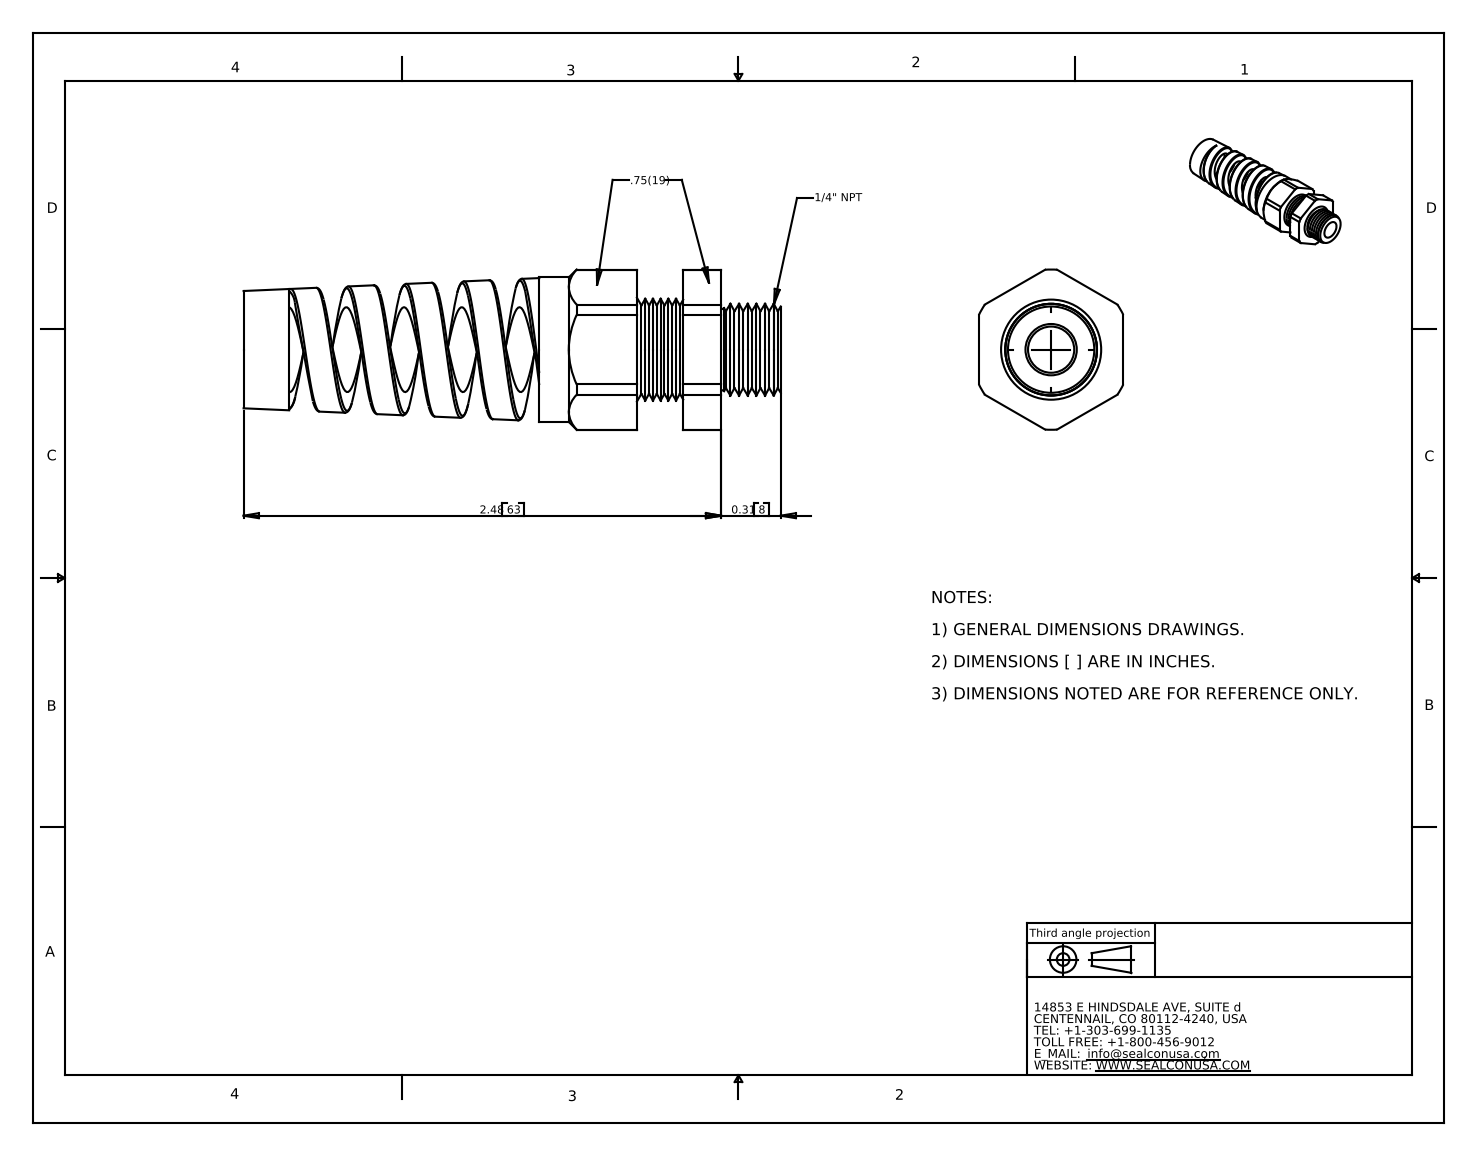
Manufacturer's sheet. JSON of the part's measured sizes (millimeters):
{"part_name": "CF07GR-GY", "step_written_by": "SolidWorks 2007 (CONFIG_CONTROL_DESIGN)", "units": "millimeters", "bodies": {"solids": 2, "faces": 144, "planar": 24, "cylindrical": 35, "other": 85}, "overall_size": [70.9, 21.2, 19.1], "volume_mm3": 8720, "surface_area_mm2": 7858, "round_holes": [[6.1, 1], [11.2, 1], [13.7, 1]], "round_bosses_or_shafts": [[19.1, 1]], "partial_cylinders_radius": [[5.9, 1], [10.6, 1]], "face_to_face_distances": [19.1, 11.1, 6.1, 5, 19.1, 12.9, 19, 24, 39, 51.9]}
